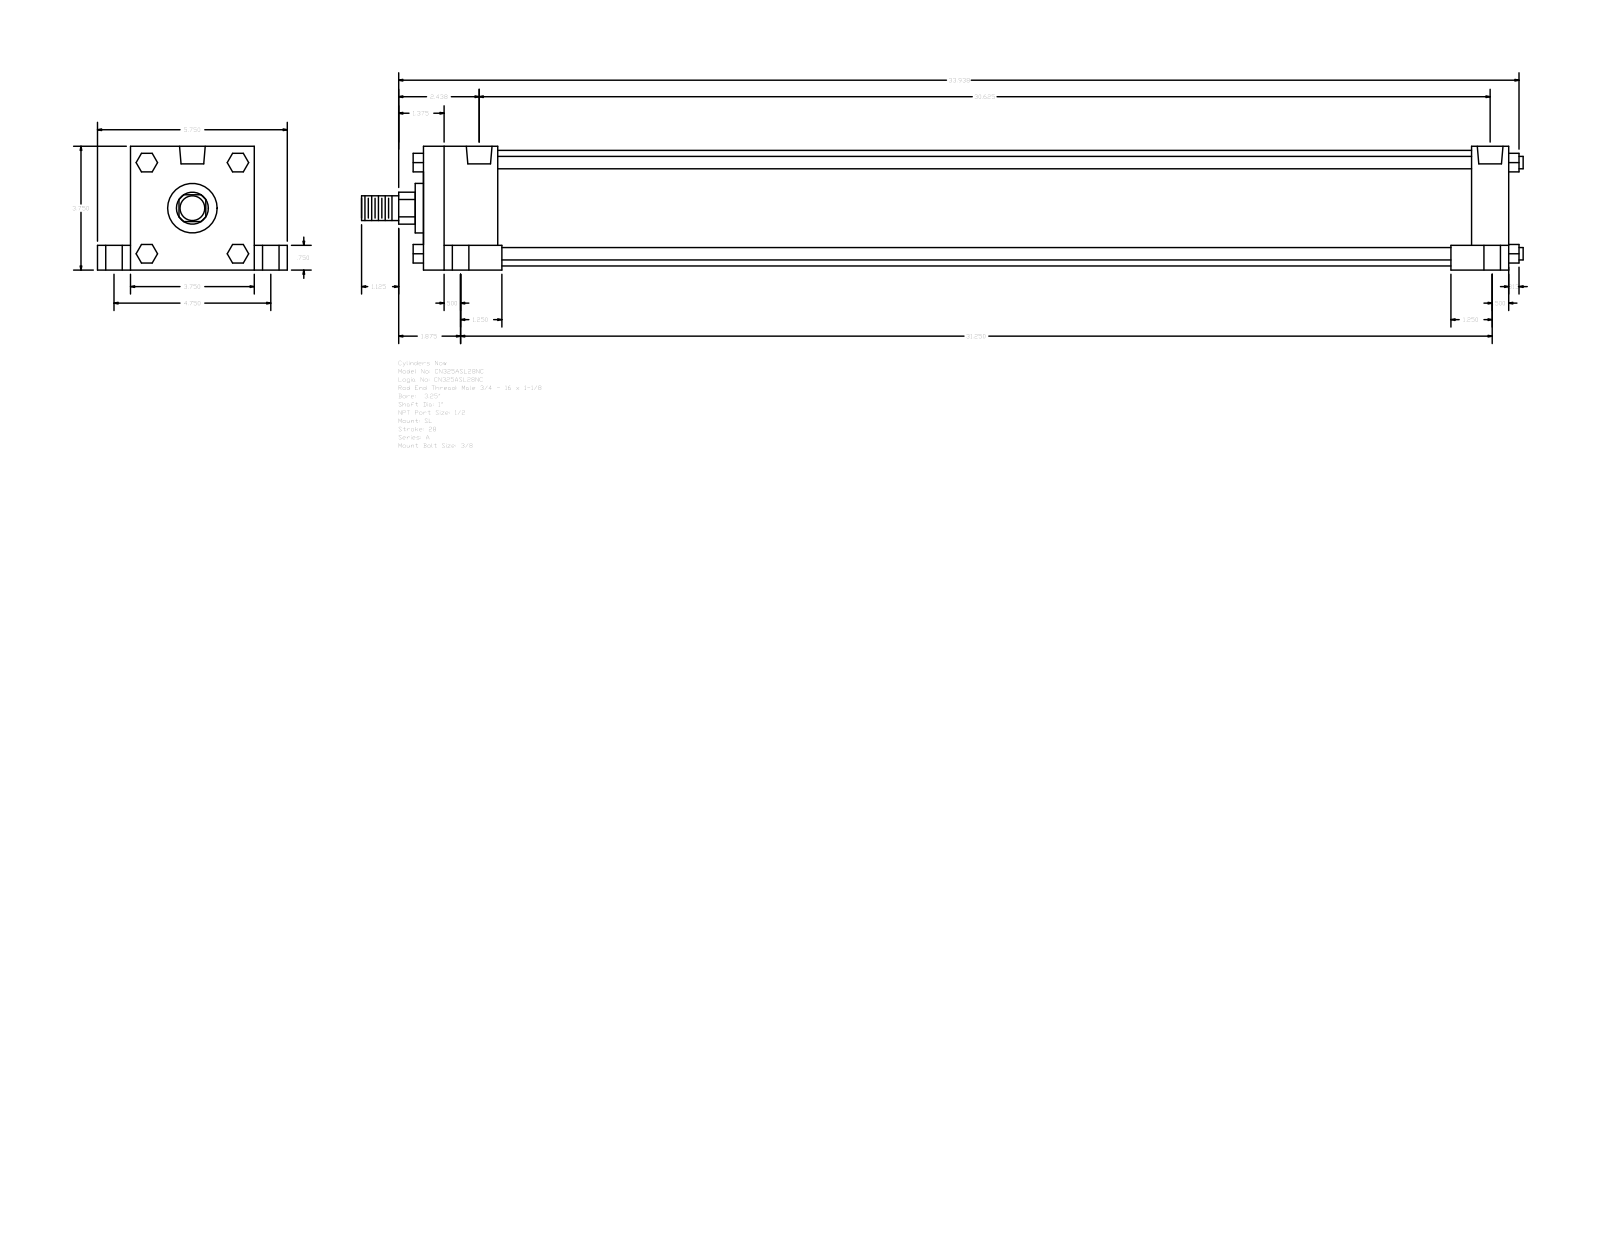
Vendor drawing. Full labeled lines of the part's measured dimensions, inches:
Part name (STEP PRODUCT): A_SL__0325_1
STEP written by: GSSL Pune (CONFIG_CONTROL_DESIGN)
Units: inches
Bodies: 0 solids, 150 faces (114 planar, 36 cylindrical, 0 other)
Overall size (bounding box): 35.187 × 5.75 × 3.75
Round holes (diameter × count): ⌀0.344 ×4, ⌀0.5 ×4, ⌀0.75 ×4, ⌀0.778 ×2
Round bosses / shafts (diameter × count): ⌀0.375 ×4, ⌀3.5 ×1, ⌀1.5 ×1, ⌀1 ×1, ⌀0.75 ×1
Partial cylindrical surfaces — rounded edges, fillets, slot ends (radius × count): R0.484 ×1
Main face-to-face distances: 3.75, 32.875, 0.75, 1, 4.75, 3, 2.25, 31.75, 29.5, 30.625
Hole centre spacings: 0.125, 2.376, 2.383, 2.441, 2.473, 4.75, 30.375, 30.5
